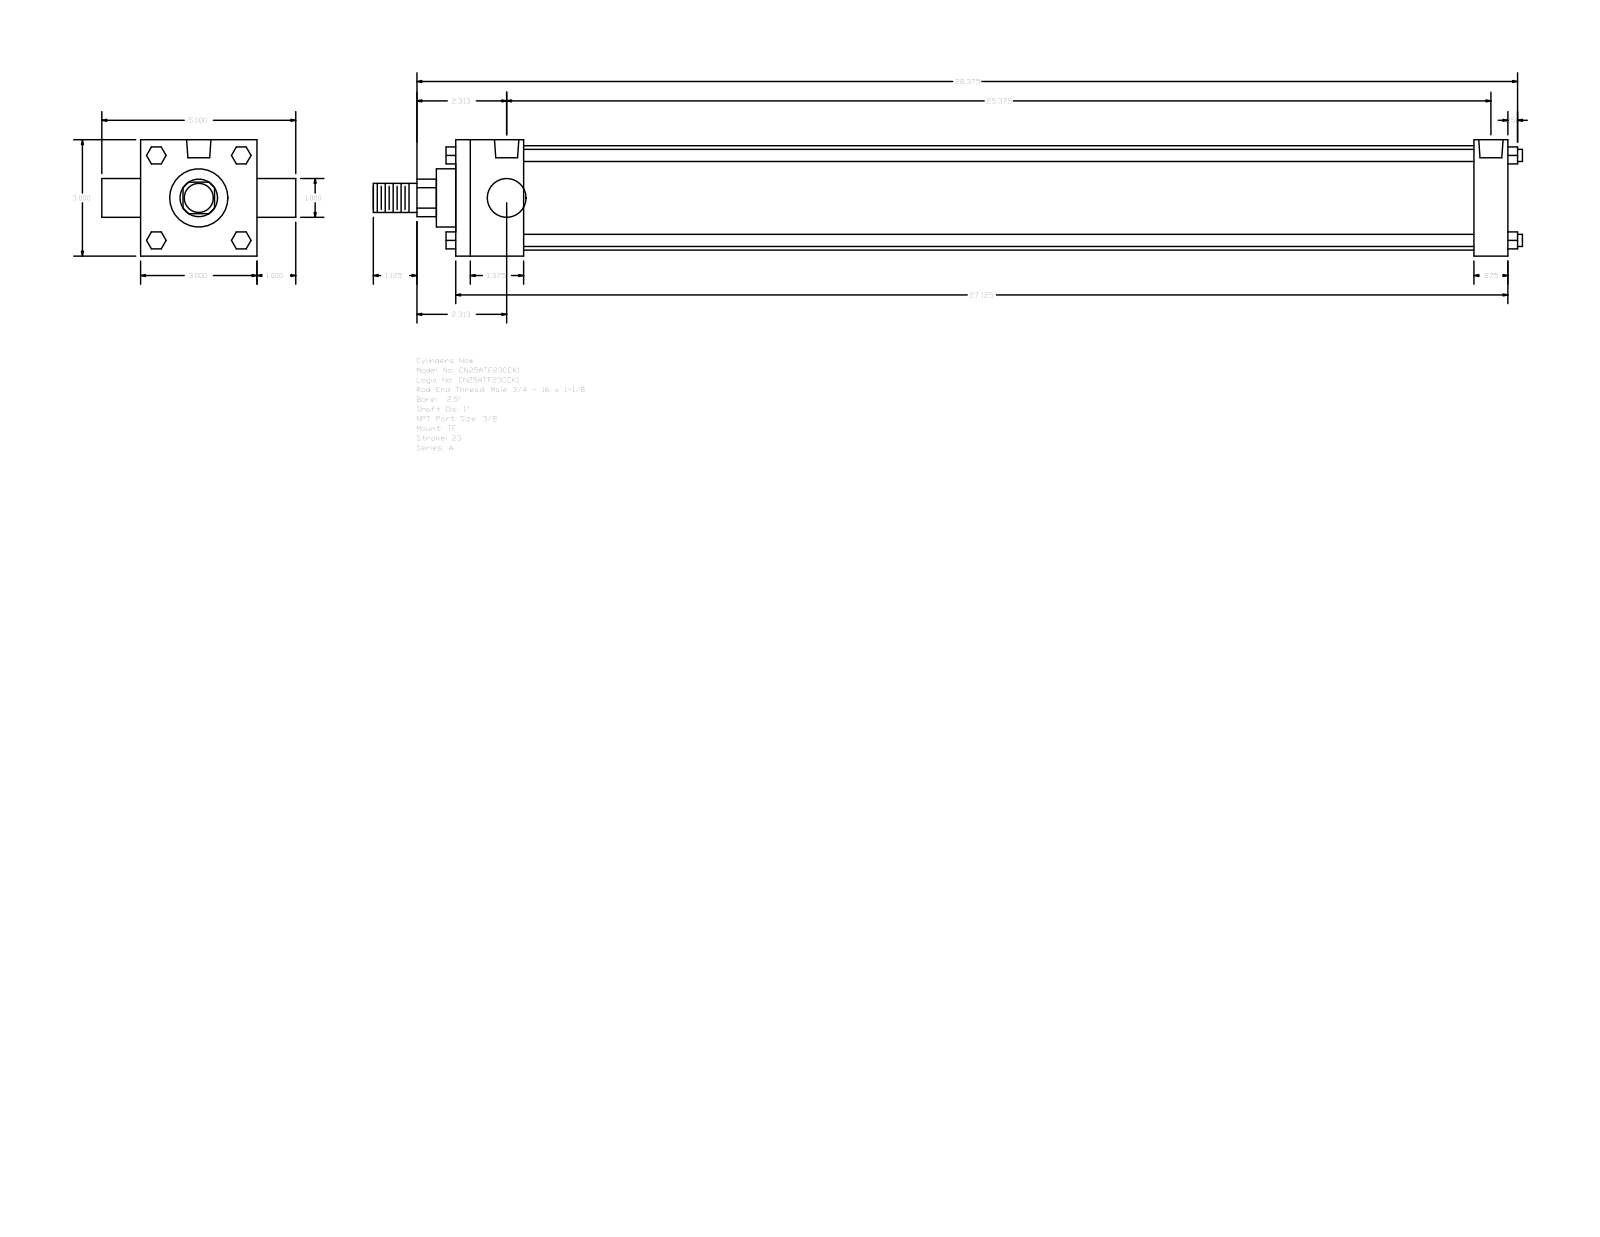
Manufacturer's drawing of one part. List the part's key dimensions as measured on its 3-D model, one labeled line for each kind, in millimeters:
Part name (STEP PRODUCT): A_TF__0250_1
STEP written by: GSSL Pune (CONFIG_CONTROL_DESIGN)
Units: millimetres
Bodies: 0 solids, 120 faces (92 planar, 28 cylindrical, 0 other)
Overall size (bounding box): 752.48 × 127 × 76.2
Round holes (diameter × count): ⌀5.56 ×3, ⌀15.93 ×2
Round bosses / shafts (diameter × count): ⌀7.94 ×4, ⌀25.4 ×2, ⌀68.33 ×1, ⌀38.1 ×1, ⌀19.05 ×1
Partial cylindrical surfaces — rounded edges, fillets, slot ends (radius × count): R12.29 ×1
Main face-to-face distances: 76.2, 688.98, 44.45, 666.75, 622.3, 644.53, 22.23, 25.4, 101.6, 701.68
Hole centre spacings: 2.38, 646.9, 644.52, 649.28
